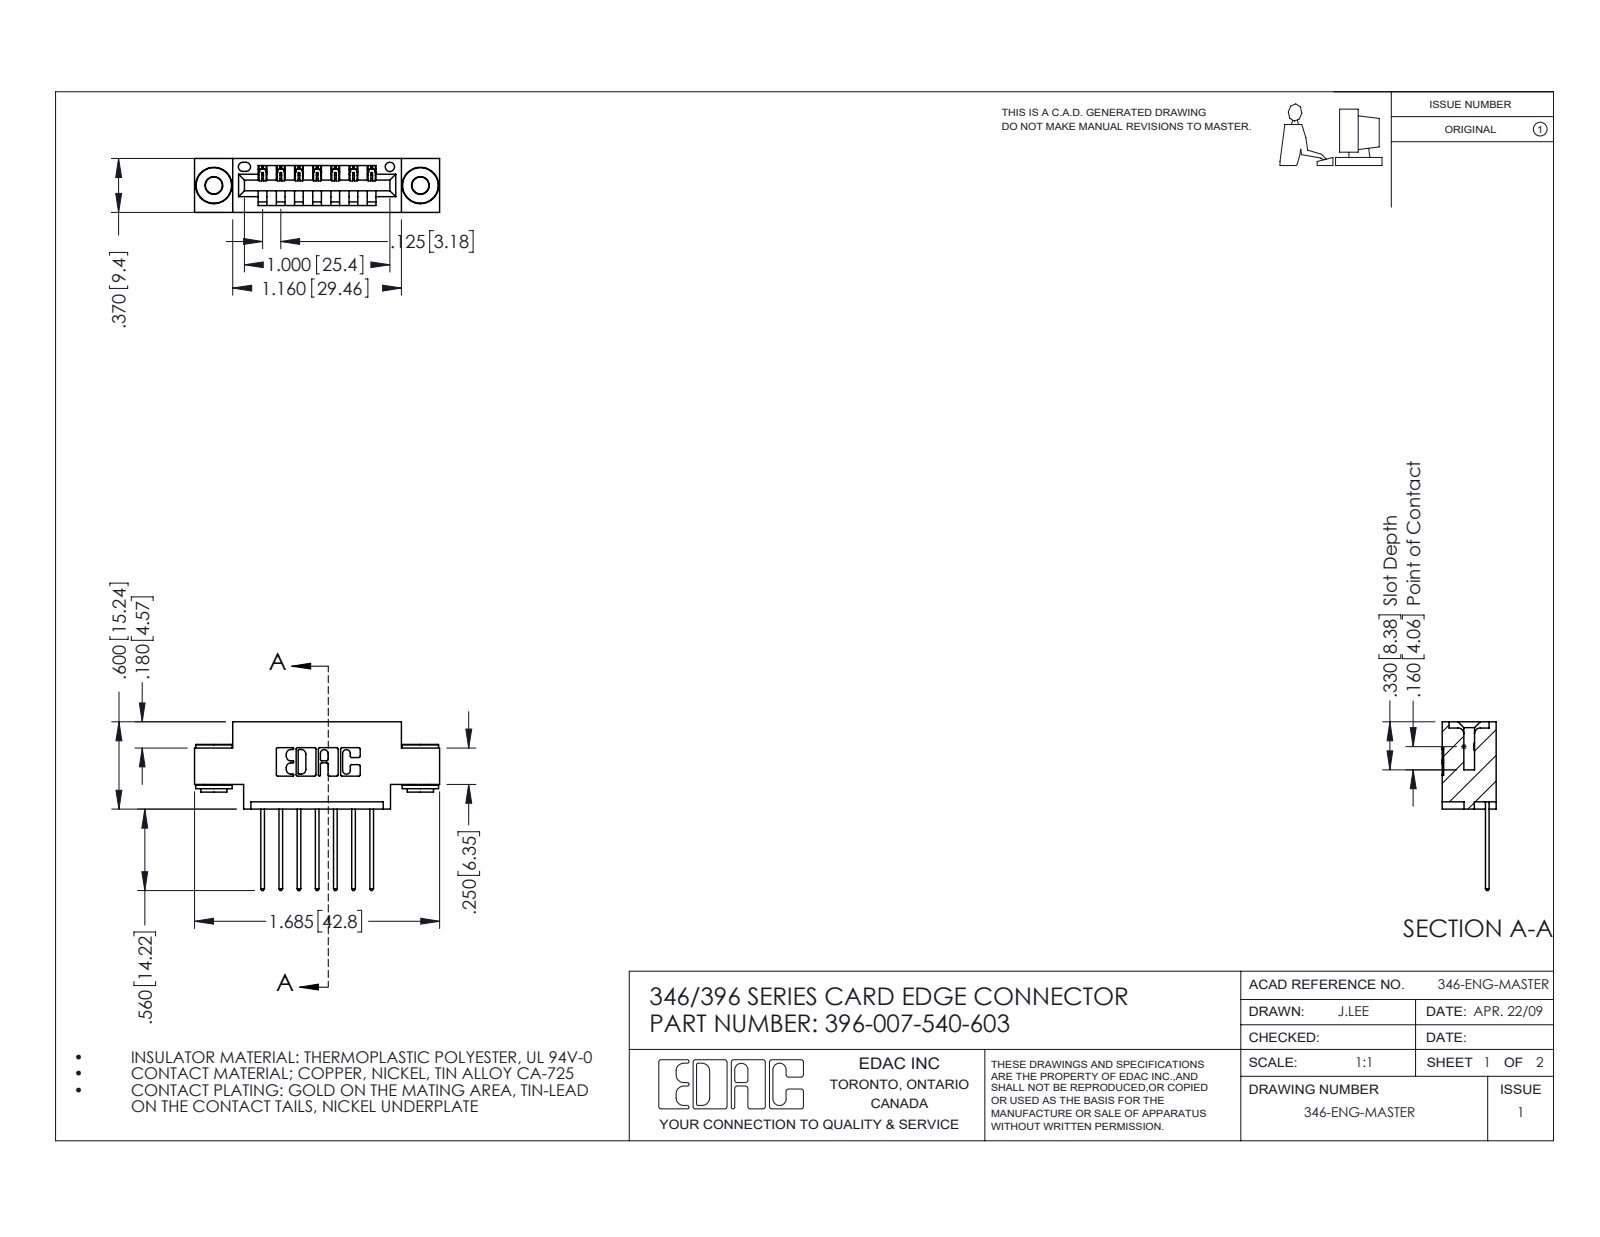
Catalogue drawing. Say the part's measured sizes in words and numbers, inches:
The part is named "396-007-540-603; 345-292-001_345-293-140; 345-250-002_345-250-002-102; 346 Part_0.170 Offset - 0.156 Dia-TH". Its 3-D file was written by "SolidWorks 2016 (CONFIG_CONTROL_DESIGN)". It is 10 solids with 570 faces: 370 planar, 192 cylindrical and 8 other. Overall it measures 1.685 by 1.16 by 0.37 inches. Its volume is 0.228 cubic inches and its surface area 7.336 square inches. Round holes: 2 of diameter 0.116, 2 of diameter 0.156, 1 of diameter 0.064. Round bosses or shafts: 2 of diameter 0.25, 2 of diameter 0.18, 2 of diameter 0.136. Partial cylindrical surfaces (rounded edges, fillets, slot ends): 22 of radius 0.01, 14 of radius 0.006, 14 of radius 0.01, 6 of radius 0.007, 6 of radius 0.031, 3 of radius 0.026, 2 of radius 0.031, 2 of radius 0.04. The main face-to-face distances are 0.25, 0.37, 0.048, 0.322, 0.025, 0.072, 0.298, 0.148, 0.222, 0.1. The hole center spacings are 0.246, 1.217, 1.42.
